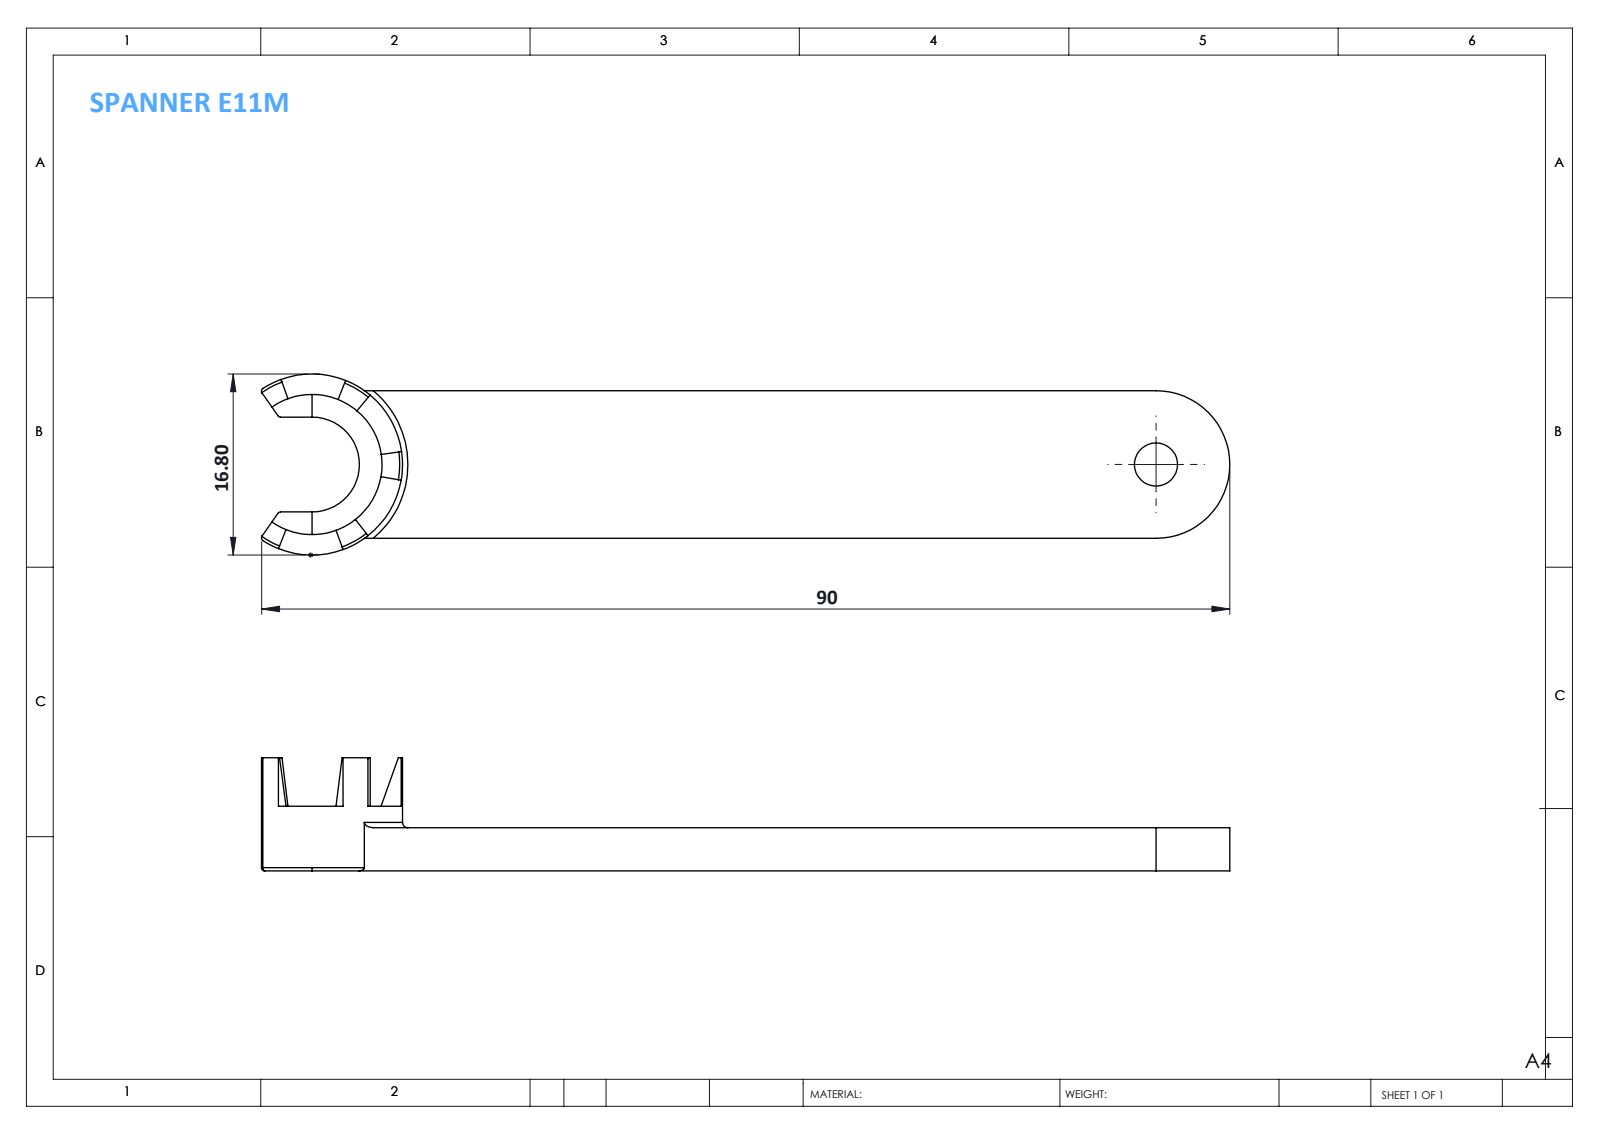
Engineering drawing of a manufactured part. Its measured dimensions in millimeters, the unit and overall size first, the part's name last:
Units: millimetres
Overall size (bounding box): 89.88 × 16.8 × 10.5
Round holes (diameter × count): ⌀4 ×1
Partial cylindrical surfaces — rounded edges, fillets, slot ends (radius × count): R0.3 ×6, R4.4 ×1, R6.85 ×1, R8.4 ×1
Main face-to-face distances: 4, 13.7, 2, 6, 2.45, 11.25, 8.8, 4.5, 6.5, 10.5
Volume: 4 751 mm³ · Surface area: 3 428 mm²
Bodies: 1 solid, 52 faces (25 planar, 13 cylindrical, 14 other)
Part name (STEP PRODUCT): SPANNER E11M
STEP written by: SolidWorks 2014 (CONFIG_CONTROL_DESIGN)
